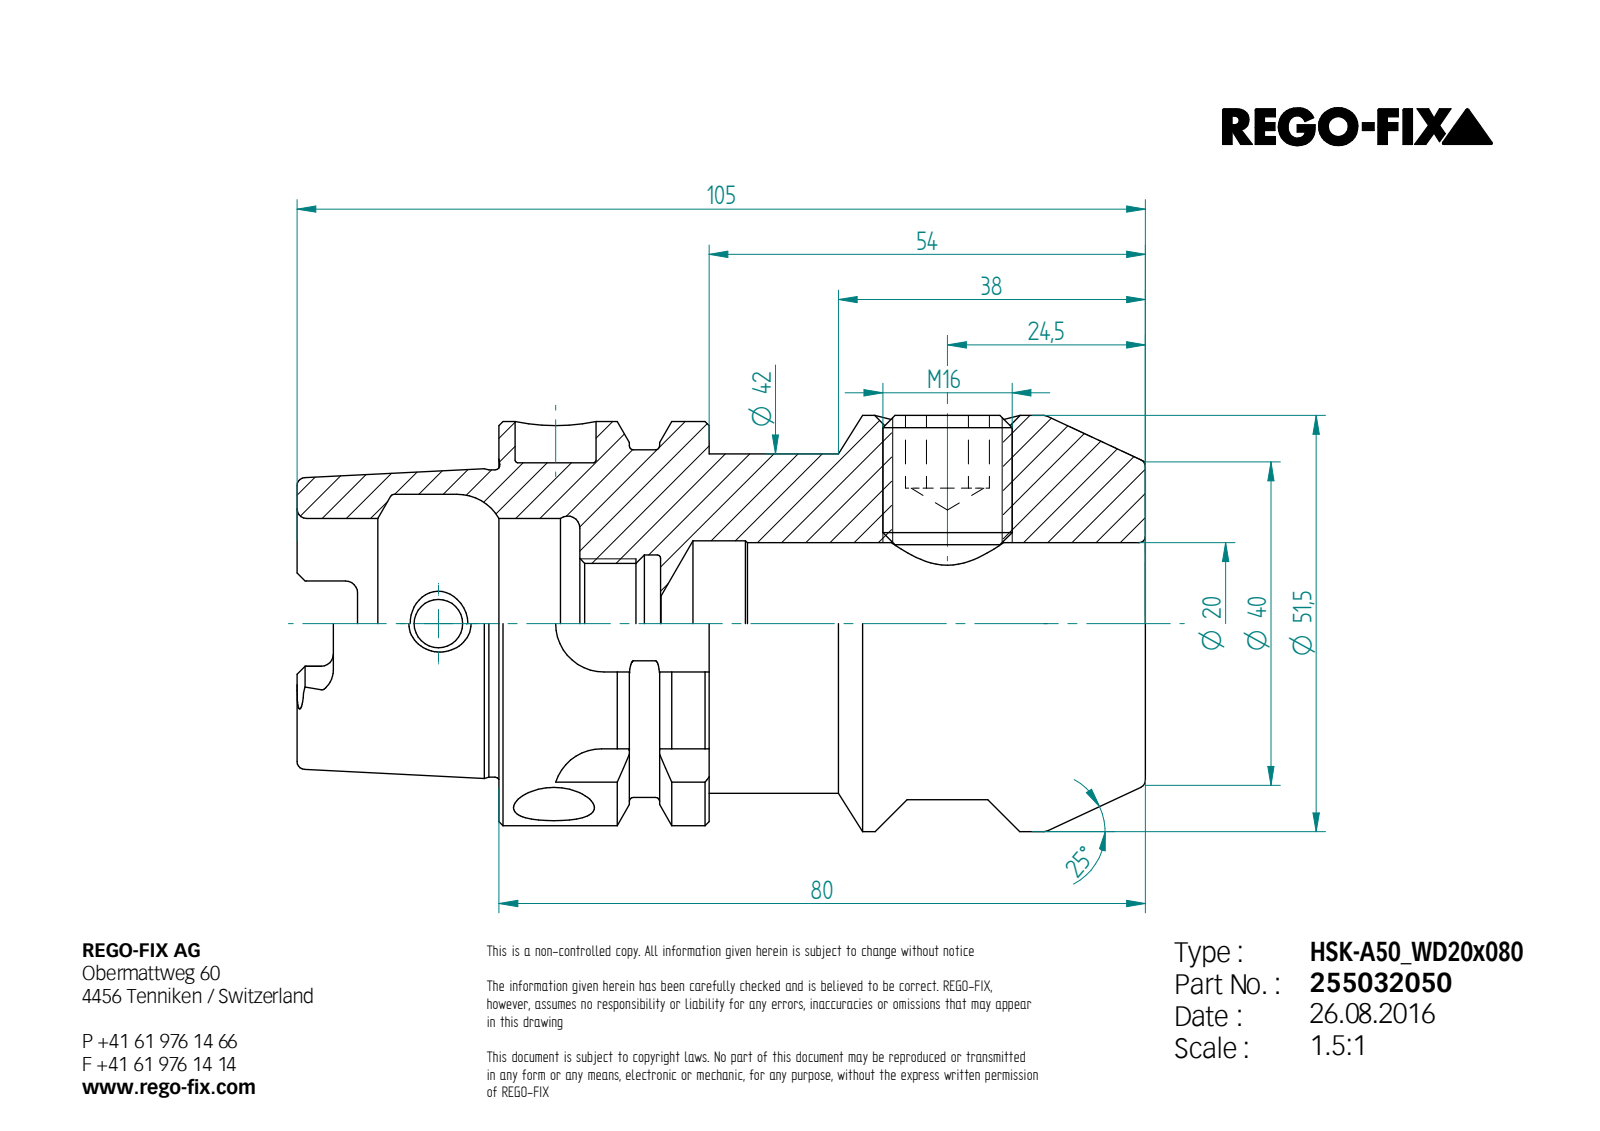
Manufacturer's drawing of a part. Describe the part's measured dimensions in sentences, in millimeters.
Its 3-D file was written by "Unknown (AUTOMOTIVE_DESIGN)". It is 3 solids with 161 faces: 65 planar, 39 cylindrical and 57 other. Overall it measures 105 by 51.5 by 51.5 millimeters. Its volume is 142 655 cubic millimeters and its surface area 33 181 square millimeters. Round holes: 2 of diameter 10, 1 of diameter 6, 1 of diameter 6.8, 1 of diameter 13.84, 1 of diameter 14.92, 1 of diameter 17, 1 of diameter 20, 1 of diameter 20.5, 1 of diameter 26, 1 of diameter 32. Round bosses or shafts: 1 of diameter 51.5, 1 of diameter 50, 1 of diameter 43, 1 of diameter 42, 1 of diameter 38.01, 1 of diameter 16. Partial cylindrical surfaces (rounded edges, fillets, slot ends): 6 of radius 1.5, 4 of radius 2.38, 4 of radius 6. The main face-to-face distances are 80, 26, 54, 10, 16, 70, 20, 42, 25, 35. The hole center spacings are 48.5.
